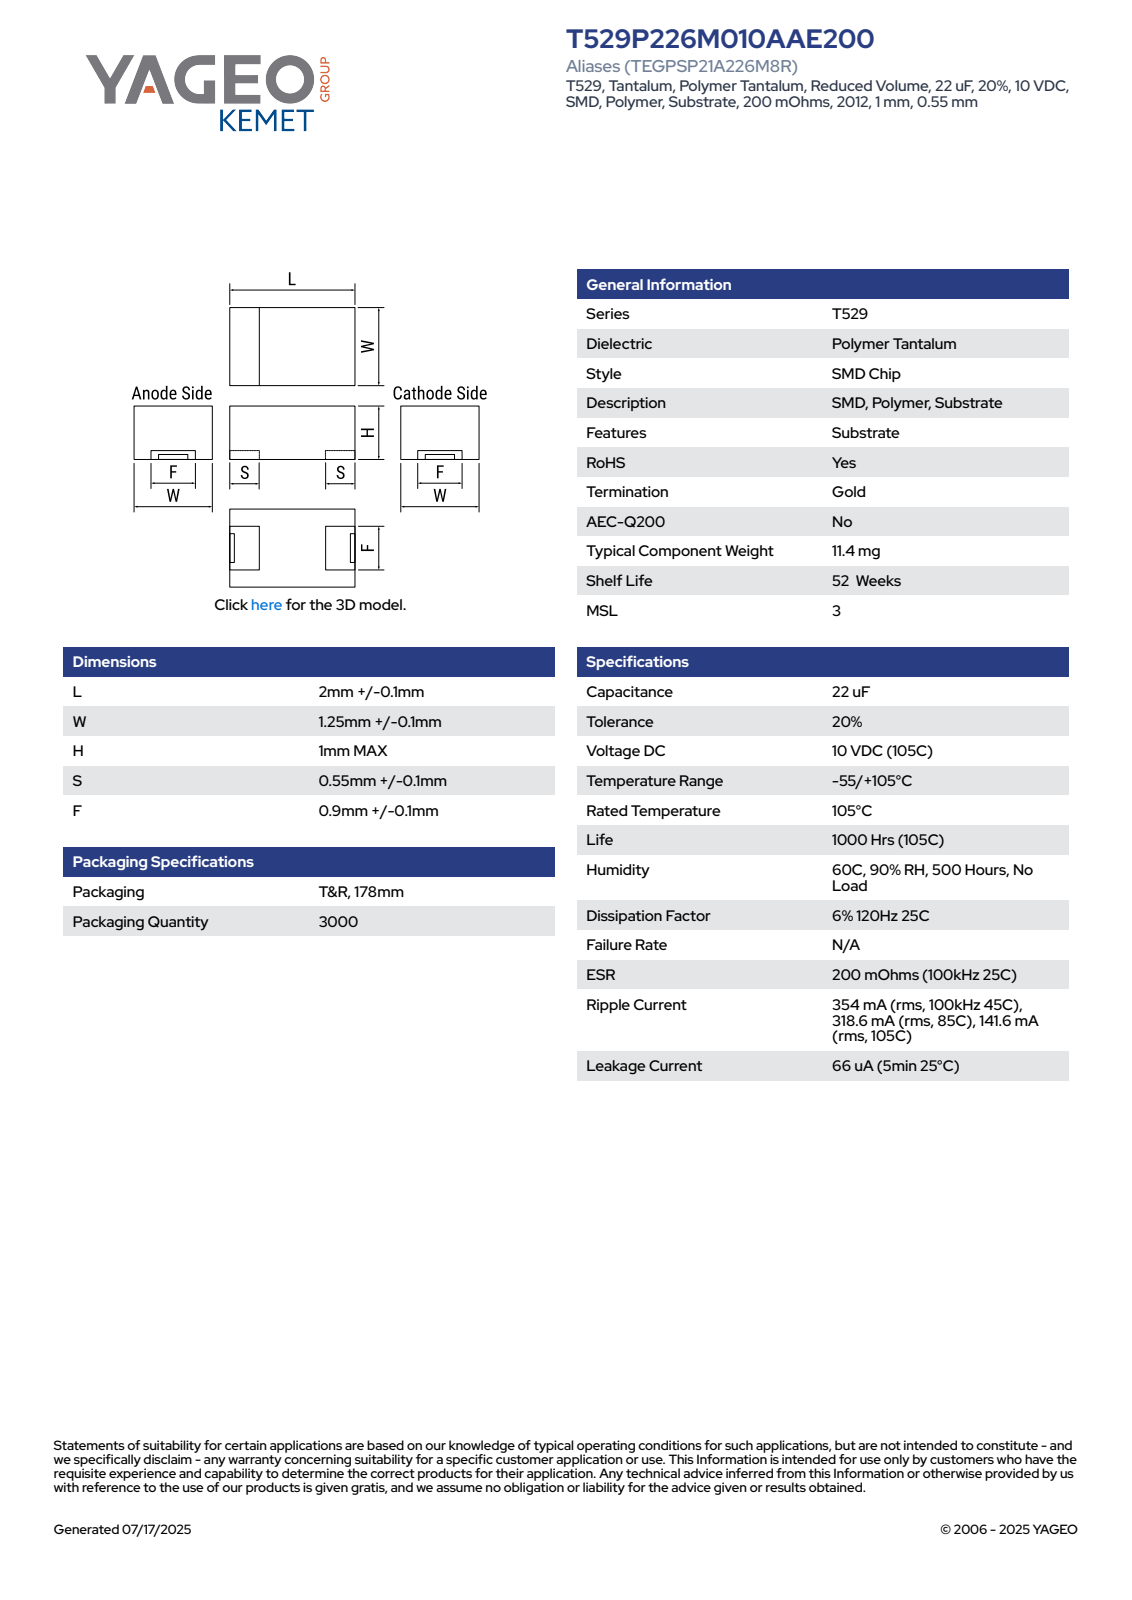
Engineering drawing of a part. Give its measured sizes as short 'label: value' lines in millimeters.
name: CTS_TCS_L2.1W1.35H1S0.55F1
written by: SolidWorks 2014 (AUTOMOTIVE_DESIGN)
unit: mm
bodies: 1 solid, 86 faces (86 planar, 0 cylindrical, 0 other)
size: 2.1 × 1.35 × 1
volume: 3 mm³; area: 14 mm²
face distances: 1, 1.35, 2.1, 0.55, 1.55, 1.18, 0.45, 2, 1.45, 1.01
